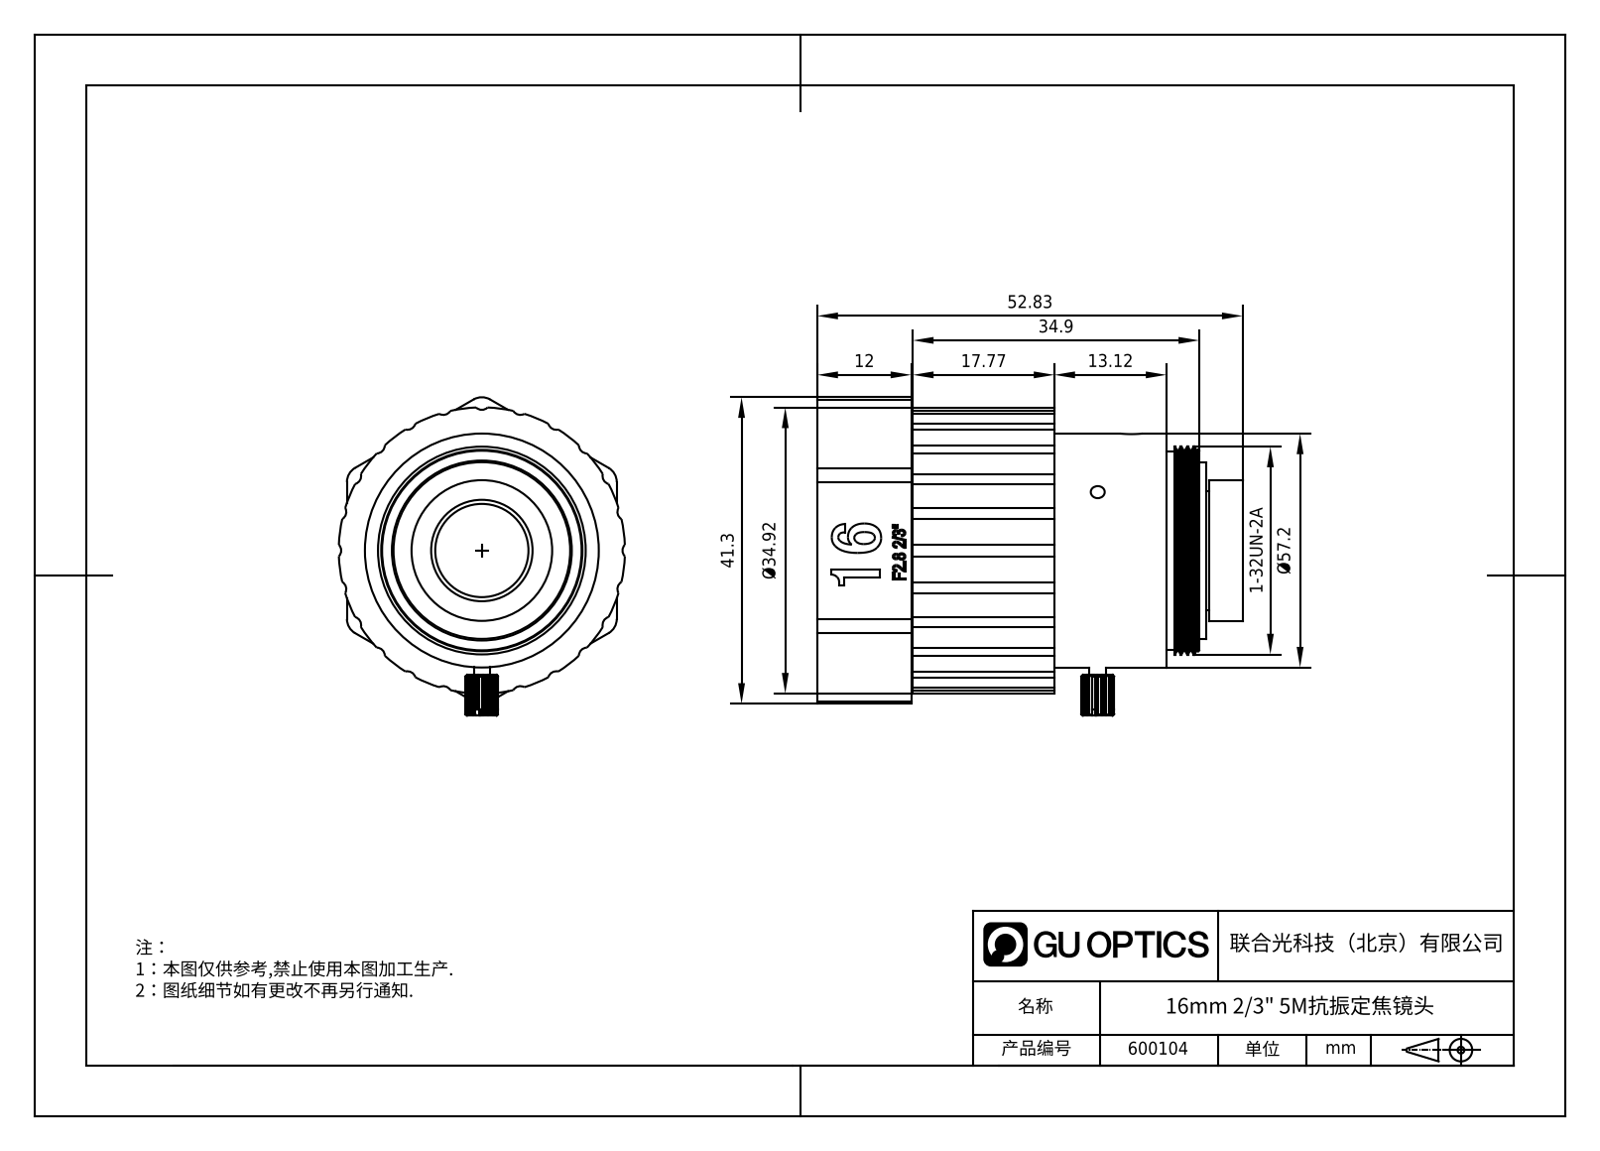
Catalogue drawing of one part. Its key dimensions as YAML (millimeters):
part_name: "600104"
step_written_by: "SolidWorks 2020 (CONFIG_CONTROL_DESIGN)"
units: millimeters
bodies: {solids: 8, faces: 389, planar: 168, cylindrical: 117, other: 104}
overall_size: [52.83, 41.3, 36.3]
volume: 60747
surface_area: 17703
round_holes:
  - {diameter: 2, count: 3}
  - {diameter: 1.7, count: 1}
  - {diameter: 2.5, count: 1}
  - {diameter: 13.1, count: 1}
  - {diameter: 16.5, count: 1}
  - {diameter: 17.3, count: 1}
  - {diameter: 22.4, count: 1}
  - {diameter: 23.2, count: 1}
  - {diameter: 25, count: 1}
  - {diameter: 25.7, count: 1}
  - {diameter: 33.4, count: 1}
round_bosses_or_shafts:
  - {diameter: 31.19, count: 1}
  - {diameter: 31, count: 1}
  - {diameter: 29.8, count: 1}
  - {diameter: 28.6, count: 1}
  - {diameter: 25.5, count: 1}
  - {diameter: 25.4, count: 1}
  - {diameter: 24.54, count: 1}
  - {diameter: 24.3, count: 1}
partial_cylinders:
  - {radius: 1, count: 24}
  - {radius: 2, count: 7}
  - {radius: 0.8, count: 2}
  - {radius: 11, count: 1}
  - {radius: 17.52, count: 1}
face_to_face_distances: [36.3, 34.9, 2.65, 2.05, 32.85, 34.77, 32.72, 4.35, 6.4, 39.12]
hole_center_spacings: [4.3]
